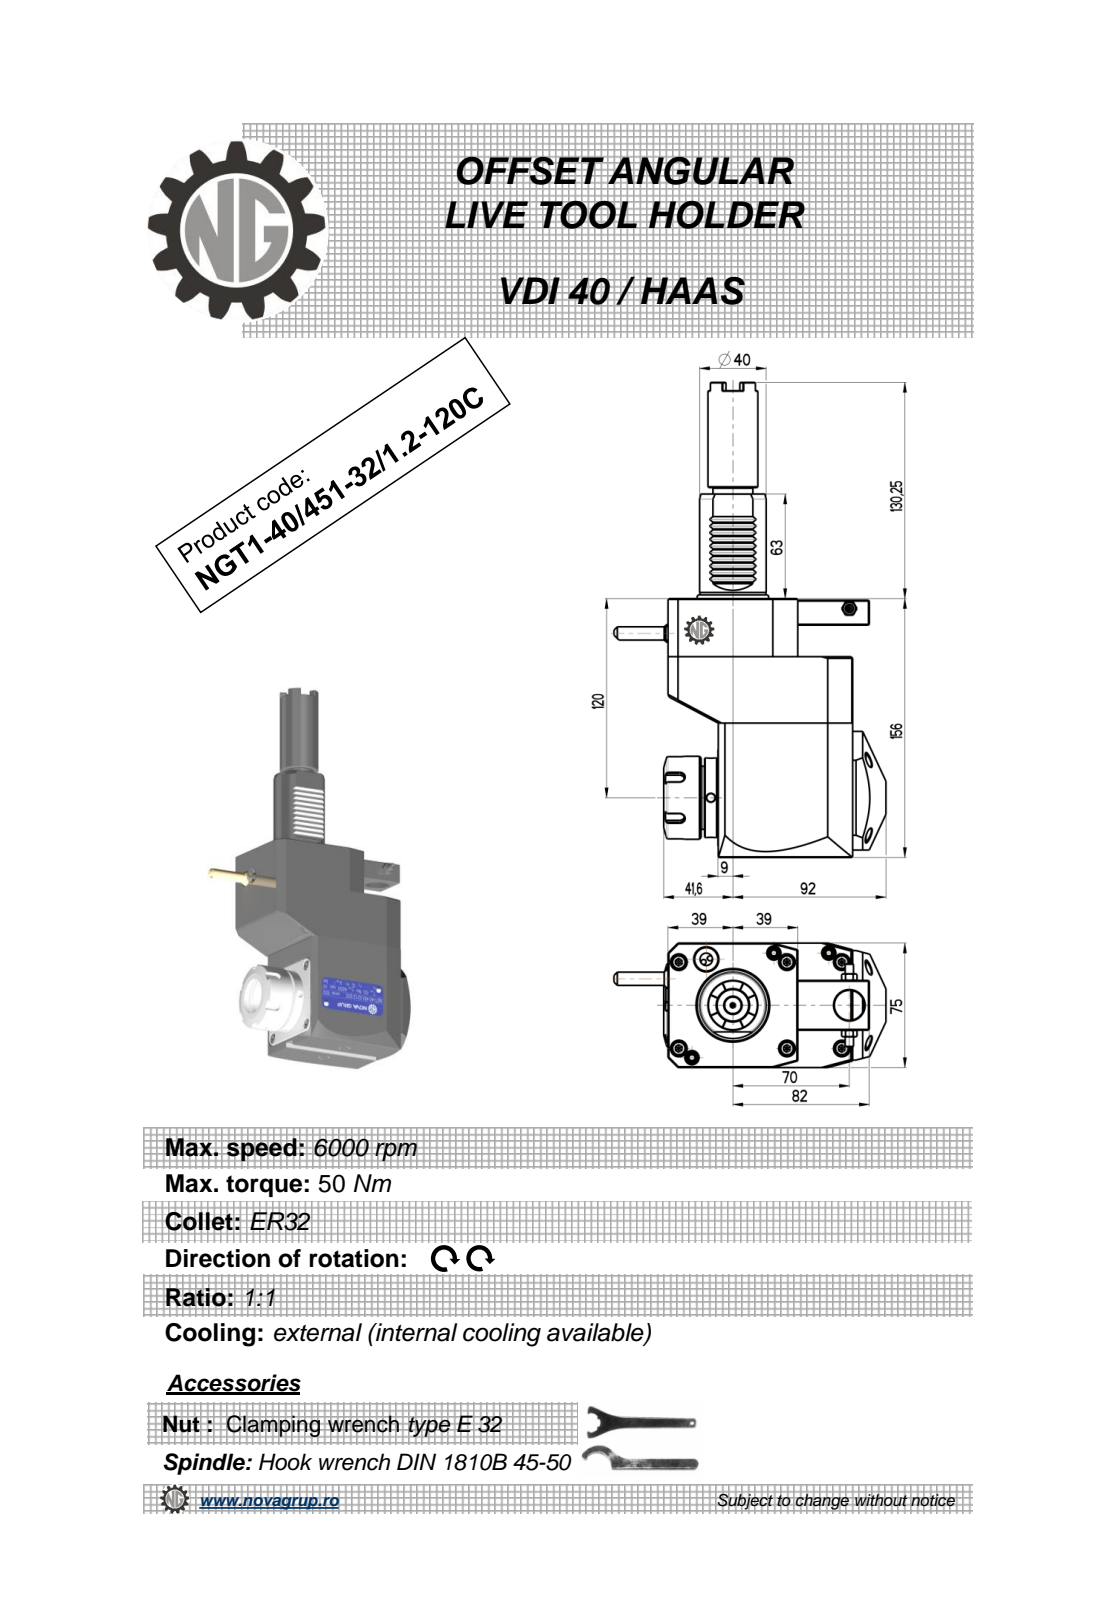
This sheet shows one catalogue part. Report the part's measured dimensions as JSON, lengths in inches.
{"part_name": "NGT1_40_451_32_1_2_120C", "step_written_by": "PRO/ENGINEER BY PARAMETRIC TECHNOLOGY CORPORATION, 2010280 (CONFIG_CONTROL_DESIGN)", "units": "inches", "bodies": {"solids": 1, "faces": 470, "planar": 234, "cylindrical": 95, "other": 141}, "overall_size": [11.27, 6.437, 3.016], "volume_in3": 75.43, "surface_area_in2": 149.9, "round_holes": [[0.197, 3], [0.118, 1], [0.165, 1], [0.374, 1], [0.709, 1], [0.768, 1], [1.055, 1], [1.063, 1]], "round_bosses_or_shafts": [[1.969, 1], [1.89, 1], [1.614, 1], [1.575, 1], [1.181, 1], [1.046, 1], [0.945, 1], [0.394, 1]], "partial_cylinders_radius": [[0.01, 12], [0.012, 10], [0.008, 6], [0.118, 5], [0.02, 1], [1.575, 1]], "face_to_face_distances": [2.953, 6.142, 4.37, 1.181, 4.764, 1.378, 3.189, 1.89, 1.299, 3.071], "hole_center_spacings": [0.522, 0.824, 2.756, 3.278, 3.948, 4.429, 5.557]}
